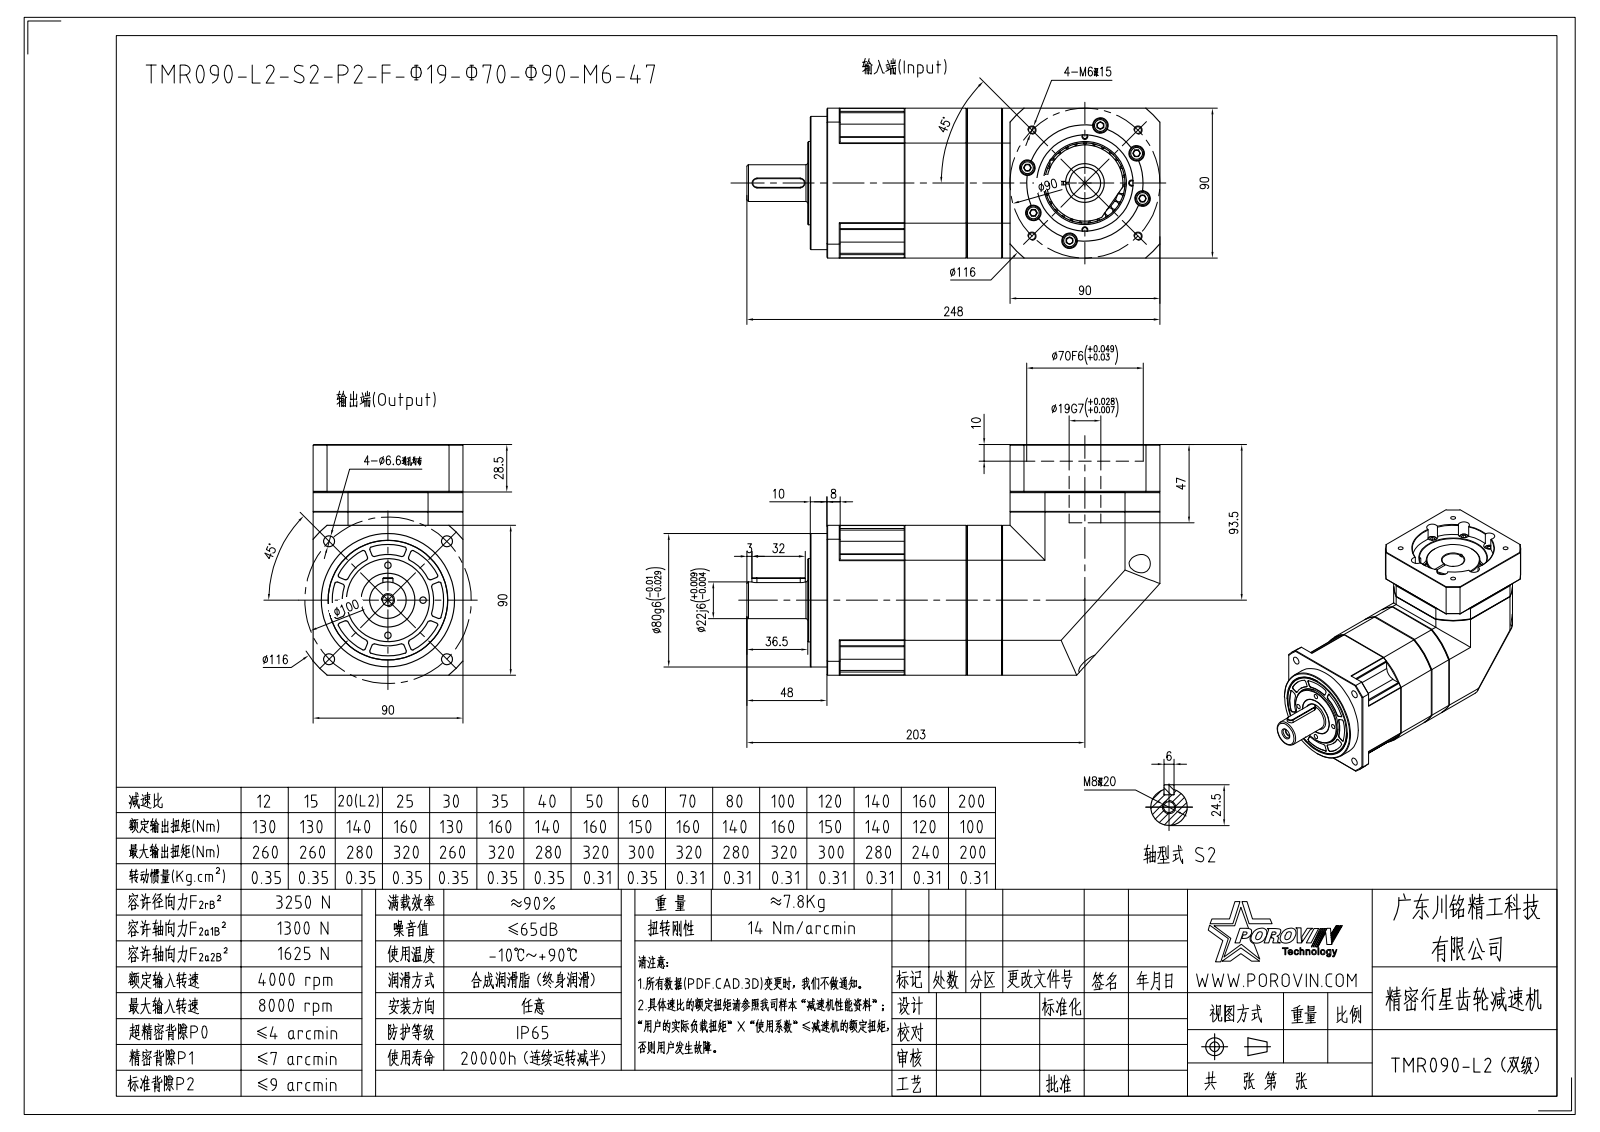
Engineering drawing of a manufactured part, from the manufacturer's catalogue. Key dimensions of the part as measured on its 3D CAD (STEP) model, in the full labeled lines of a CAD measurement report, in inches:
Part name (STEP PRODUCT): M900001; HEXAGON_SOCKET_HEAD_CAP_SC-9564; SPRING_LOCK_WASHERS--NORM-19349; HEXAGON_SOCKET_HEAD_CAP_S-19443 (+8 more)
STEP written by: CREO PARAMETRIC BY PTC INC, 2020053 (CONFIG_CONTROL_DESIGN)
Units: inches
Bodies: 43 solids, 1321 faces (526 planar, 561 cylindrical, 234 other)
Overall size (bounding box): 9.764 × 5.453 × 3.543
Volume: 98.25 in³ · Surface area: 369.8 in²
Round holes (diameter × count): ⌀0.213 ×12, ⌀0.217 ×12, ⌀0.374 ×12, ⌀0.26 ×10, ⌀0.165 ×7, ⌀0.197 ×5, ⌀0.256 ×5, ⌀0.157 ×4, ⌀0.263 ×4, ⌀0.433 ×4, ⌀0.268 ×1, ⌀0.331 ×1
Round bosses / shafts (diameter × count): ⌀0.335 ×12, ⌀0.315 ×12, ⌀0.197 ×12, ⌀0.394 ×4, ⌀0.389 ×4, ⌀0.236 ×4, ⌀3.15 ×1, ⌀3.071 ×1
Partial cylindrical surfaces — rounded edges, fillets, slot ends (radius × count): R0.039 ×92, R0.295 ×4, R2.008 ×3, R0.118 ×2, R2.283 ×2, R0.157 ×1, R0.207 ×1, R0.817 ×1
Main face-to-face distances: 3.543, 0.472, 0.846, 0.839, 1.476, 2.315, 2.323, 4.331, 0.394, 1.024
Hole centre spacings: 1.407, 1.077, 1.502, 1.732, 2.601, 2.619, 2.532, 3.152
